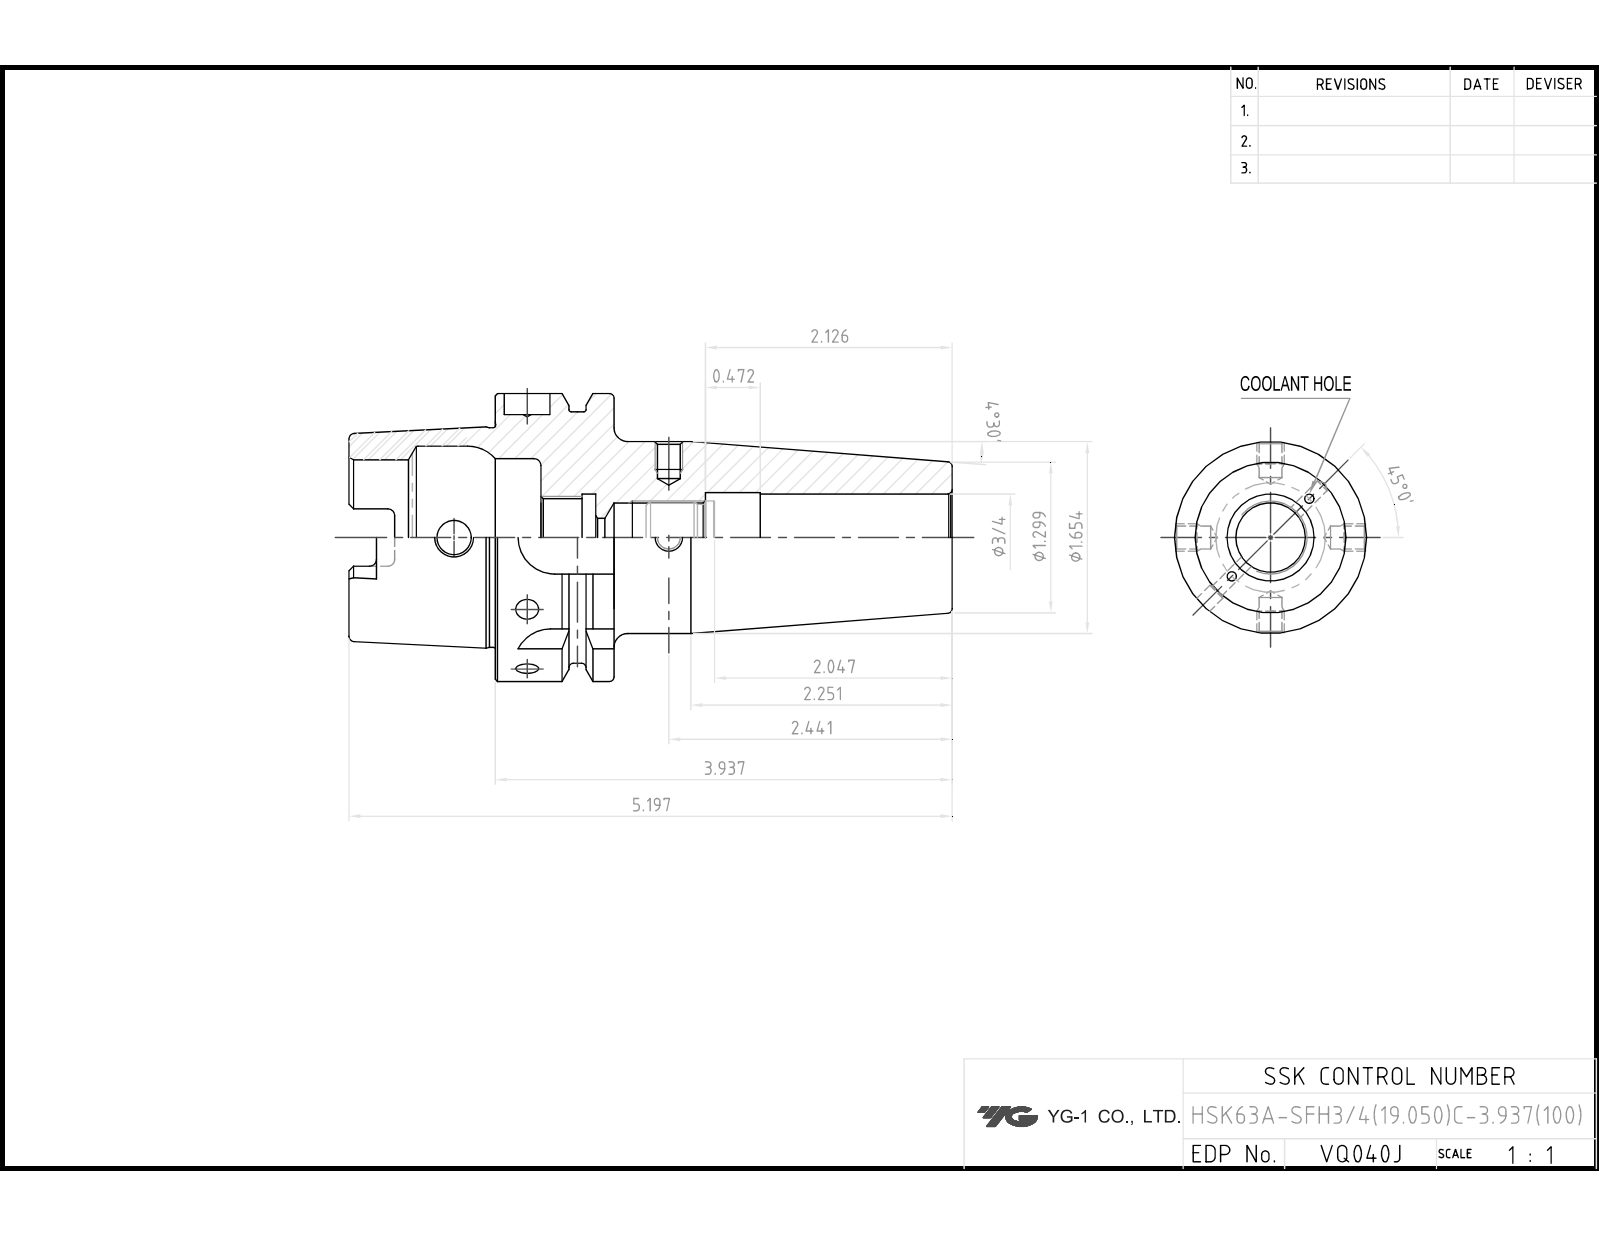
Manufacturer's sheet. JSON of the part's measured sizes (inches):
{"part_name": "HSK63A_BALANCE_20200217", "step_written_by": "CREO PARAMETRIC BY PTC INC, 2018500 (CONFIG_CONTROL_DESIGN)", "units": "inches", "bodies": {"solids": 1, "faces": 184, "planar": 57, "cylindrical": 57, "other": 70}, "overall_size": [5.197, 2.48, 2.48], "volume_in3": 9.069, "surface_area_in2": 56.49, "round_holes": [[0.197, 2], [0.295, 1], [0.331, 1], [0.394, 1], [0.591, 1], [0.63, 1], [0.669, 1], [0.709, 1], [0.748, 1], [0.75, 1], [0.774, 1], [1.339, 1]], "round_bosses_or_shafts": [[2.48, 1], [2.165, 1], [1.891, 1], [1.654, 1]], "partial_cylinders_radius": [[0.059, 6], [0.113, 4], [0.315, 4]], "face_to_face_distances": [1.024, 0.394, 0.63, 1.26, 3.543, 3.937, 2.913, 1.654, 2.283, 0.241]}
